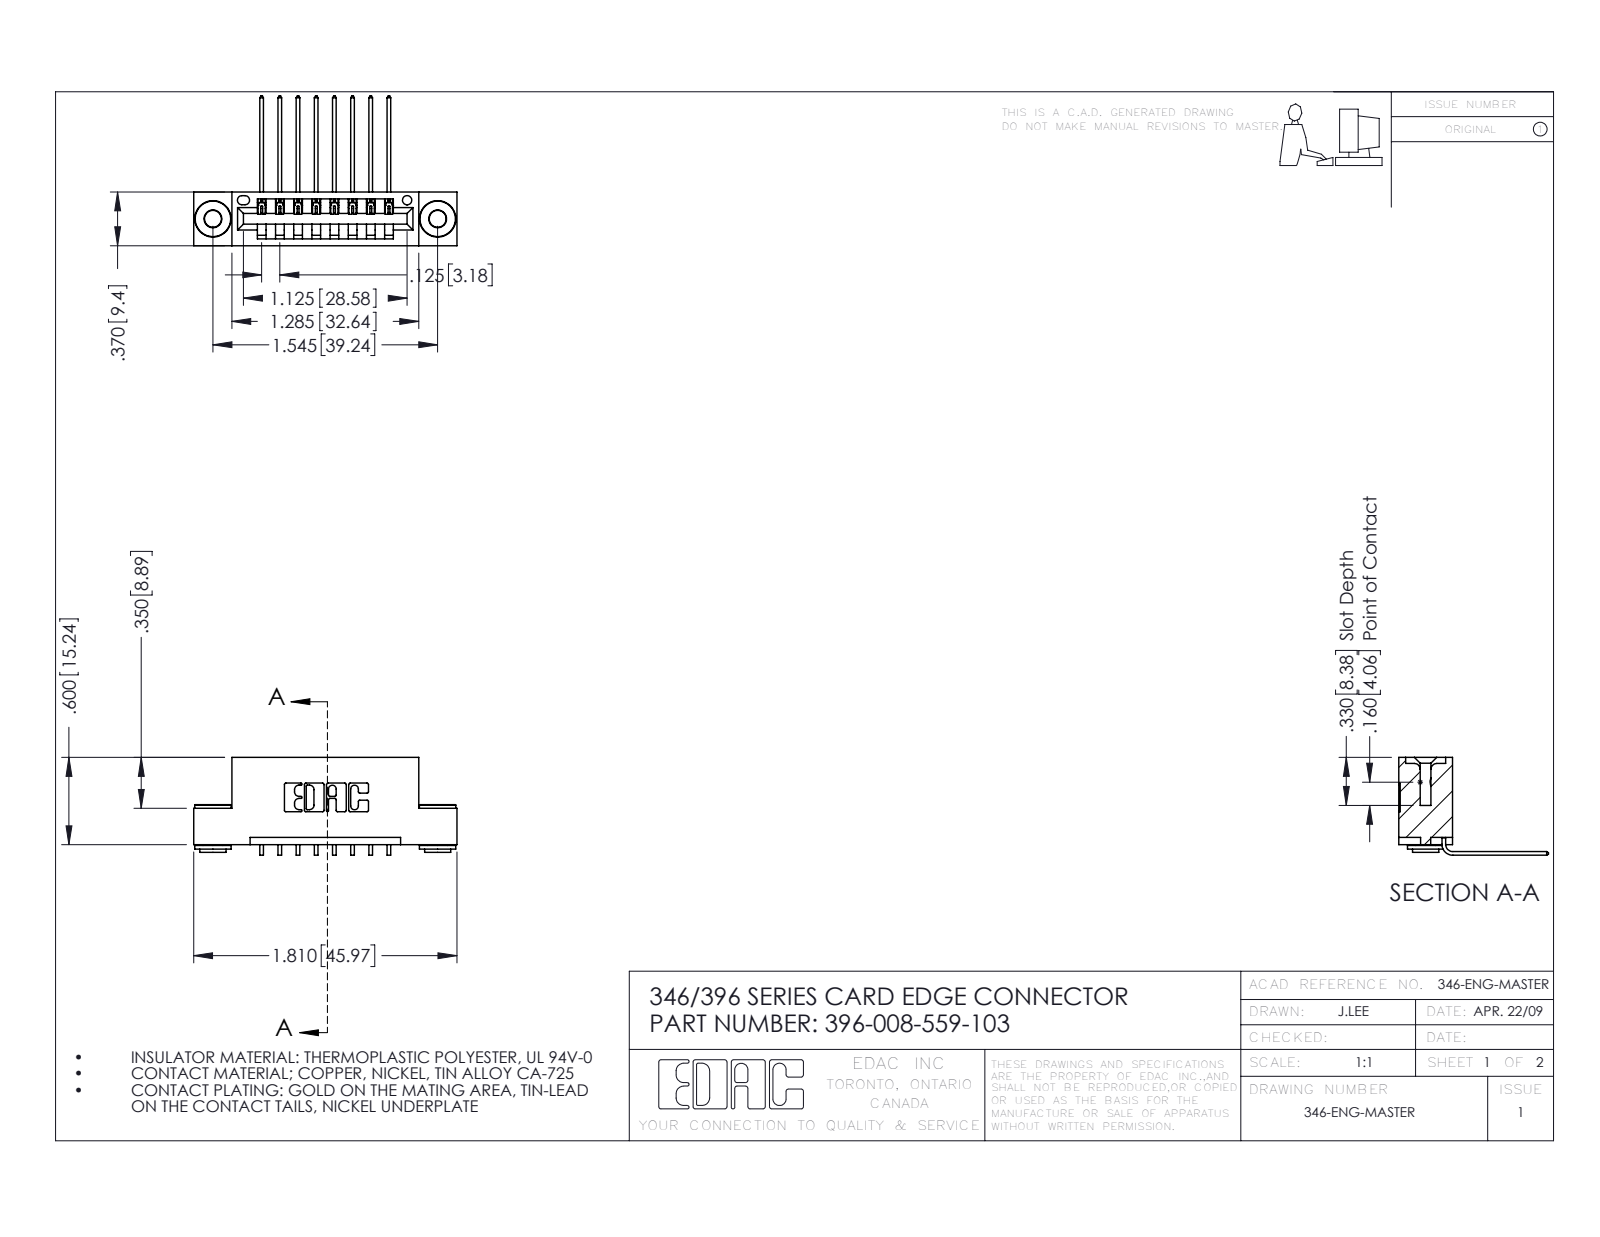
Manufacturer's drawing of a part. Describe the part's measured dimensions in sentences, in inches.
The part is named "345-250-002_345-250-002-102; 346 Part_Flush Mounting Lugs - 0.156 Dia-TH; 345-292-001_558 559 Tail - 1; 396-008-559-103". Its 3-D file was written by "SolidWorks 2016 (CONFIG_CONTROL_DESIGN)". It is 11 solids with 640 faces: 422 planar, 210 cylindrical and 8 other. Overall it measures 1.81 by 1.03 by 0.673 inches. Its volume is 0.257 cubic inches and its surface area 8.178 square inches. Round holes: 2 of diameter 0.116, 2 of diameter 0.156, 1 of diameter 0.064. Round bosses or shafts: 2 of diameter 0.25, 2 of diameter 0.18, 2 of diameter 0.136. Partial cylindrical surfaces (rounded edges, fillets, slot ends): 22 of radius 0.01, 16 of radius 0.006, 6 of radius 0.007, 6 of radius 0.031, 3 of radius 0.026, 2 of radius 0.031, 2 of radius 0.04, 1 of radius 0.014. The main face-to-face distances are 0.25, 0.048, 0.322, 0.37, 0.025, 0.072, 0.298, 0.5, 0.148, 0.222. The hole center spacings are 0.246, 1.341, 1.545.
